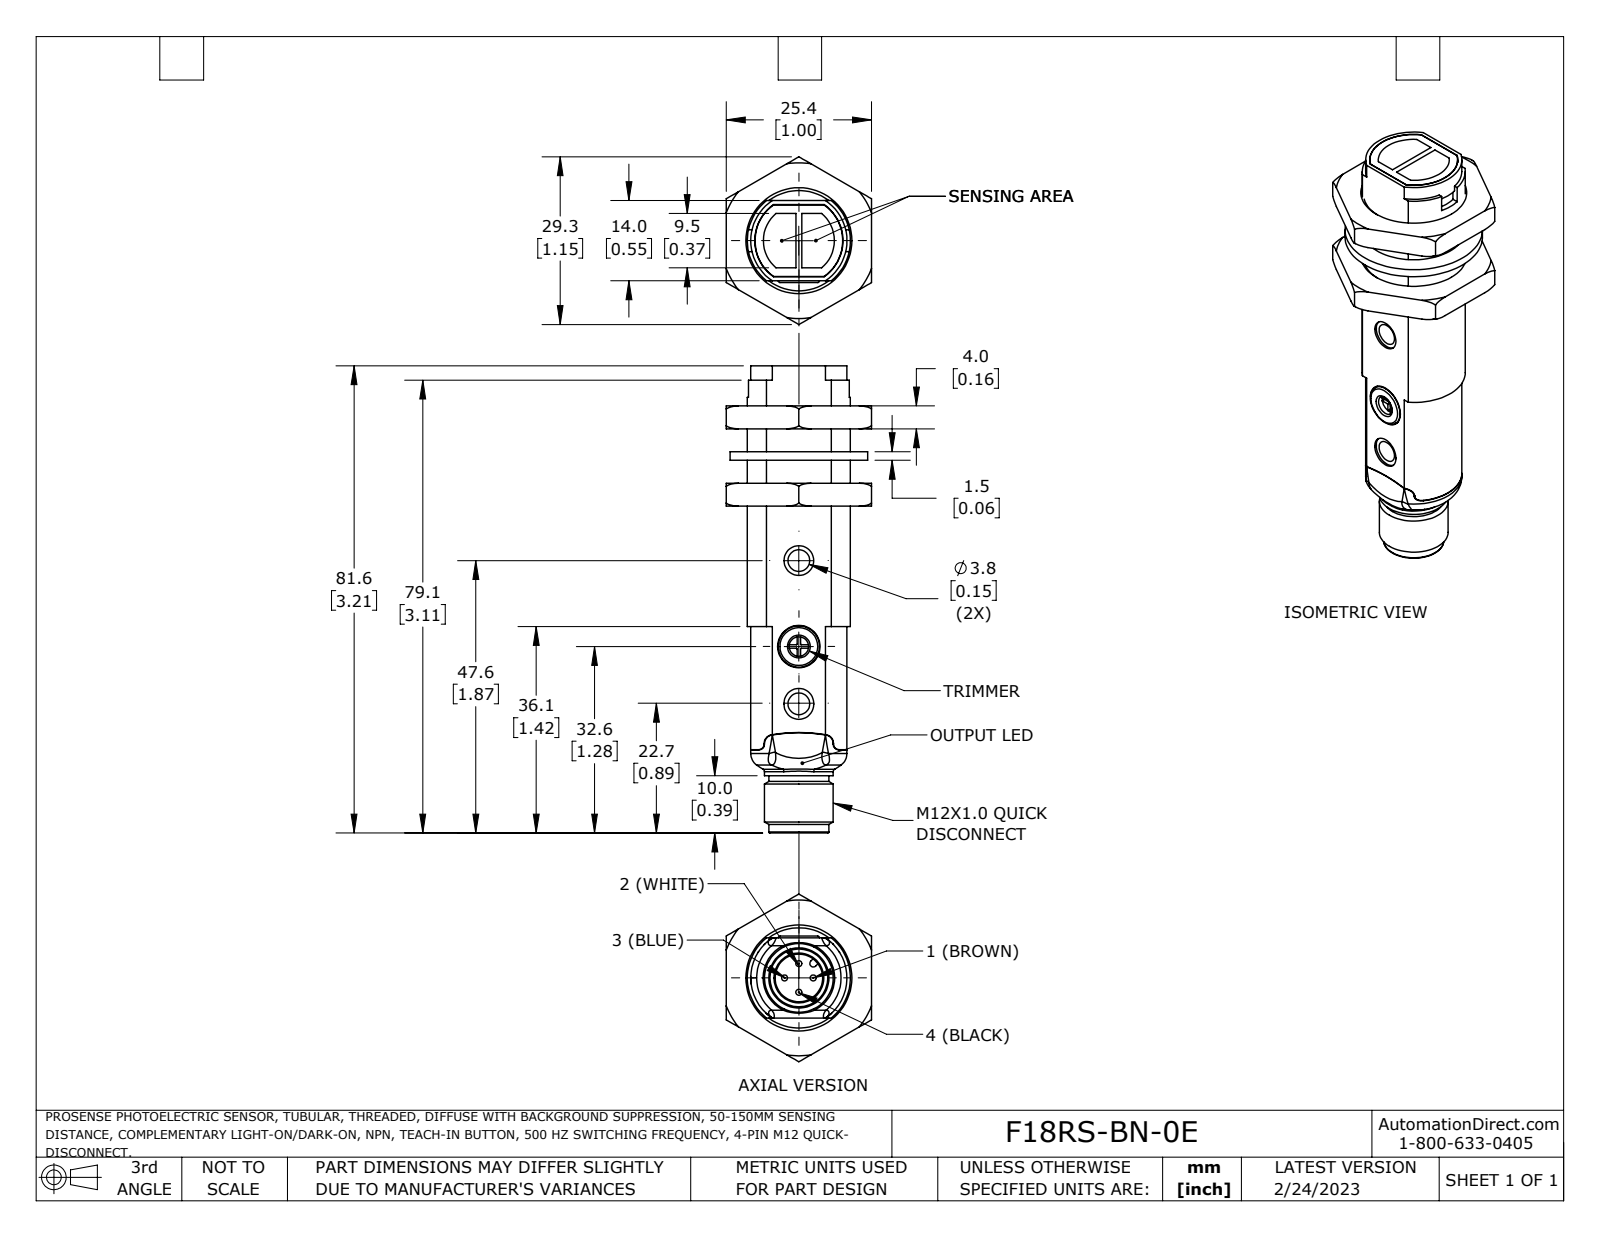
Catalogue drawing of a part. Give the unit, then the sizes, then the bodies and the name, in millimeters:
Units: millimetres
Overall size (bounding box): 81.55 × 29.28 × 25.36
Round holes (diameter × count): ⌀3.8 ×2, ⌀3.4 ×1, ⌀5.2 ×1, ⌀7.4 ×1, ⌀17.5 ×1
Round bosses / shafts (diameter × count): ⌀1.05 ×4, ⌀24 ×1, ⌀18 ×1, ⌀12 ×1, ⌀10.5 ×1, ⌀7.2 ×1
Partial cylindrical surfaces — rounded edges, fillets, slot ends (radius × count): R1 ×4, R1.5 ×4, R2.6 ×2, R28 ×2, R0.5 ×1, R0.6 ×1, R7.65 ×1, R7.7 ×1
Main face-to-face distances: 4, 9.5, 14, 13.5, 5.5, 8, 25.36, 17.5, 11, 1.5
Hole centre spacings: 10, 15, 25
Volume: 18 292 mm³ · Surface area: 8 376 mm²
Bodies: 4 solids, 206 faces (87 planar, 58 cylindrical, 61 other)
Part name (STEP PRODUCT): F18RS-BN-0E
STEP written by: SolidWorks 2021 (AUTOMOTIVE_DESIGN)
